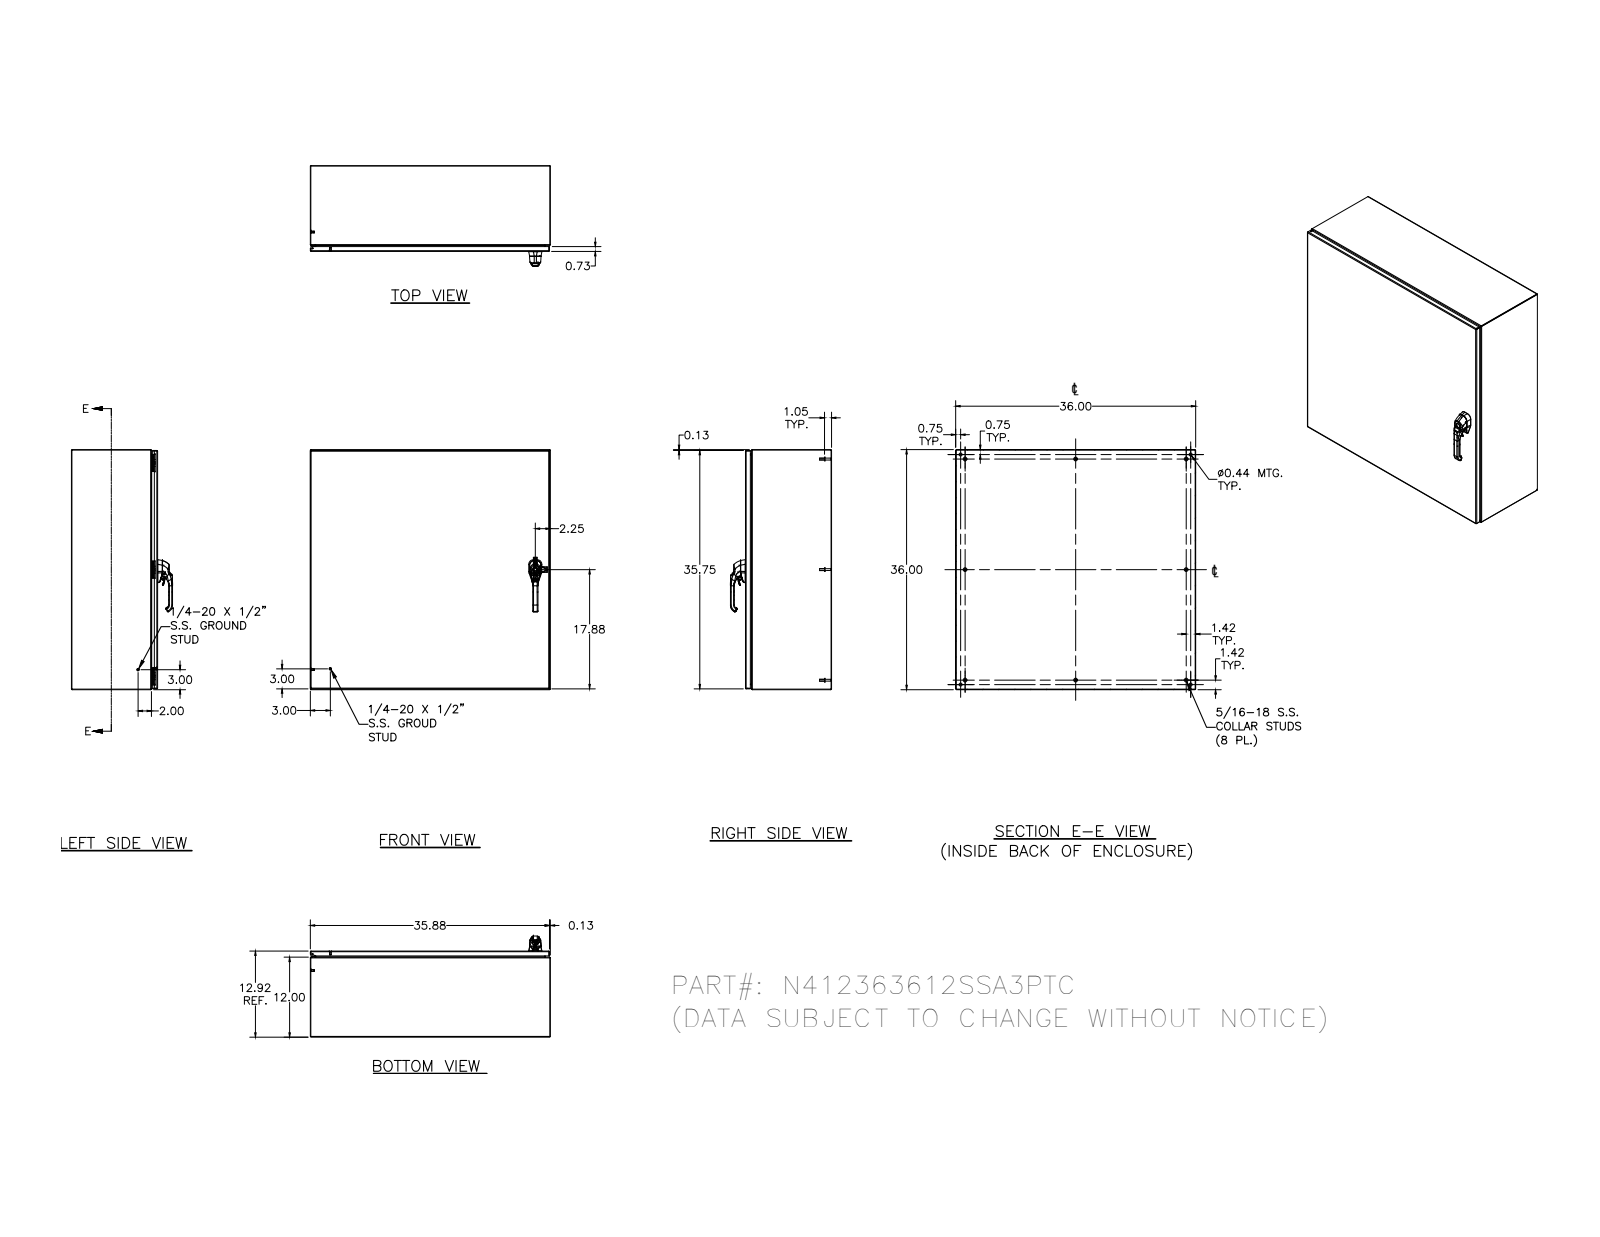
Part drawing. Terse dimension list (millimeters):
name: N412363612SSA3PTC; N412363612SSA3PTCBTB; N4123612SSA3PTCLS; N4123612SSA3PTCRS (+8 more)
written by: Autodesk Inventor 2011 (AUTOMOTIVE_DESIGN)
unit: mm
bodies: 72 solids, 3436 faces (1153 planar, 1265 cylindrical, 1018 other)
size: 914.4 × 914.4 × 385.2
volume: 5 752 000 mm³; area: 6 057 000 mm²
holes: 6× ⌀2.4, 6× ⌀3.9, 6× ⌀4.2, 6× ⌀4.4, 6× ⌀4.7, 5× ⌀4.2, 4× ⌀11.1, 3× ⌀4, 3× ⌀5.4, 2× ⌀2.7, 2× ⌀4.1, 2× ⌀4.3
bosses: 14× ⌀6.4, 8× ⌀14.3, 8× ⌀7.6, 8× ⌀7, 6× ⌀9.1, 6× ⌀8.1, 6× ⌀6.5, 6× ⌀4.2
rounds: 188× R0.5, 100× R0.3, 38× R1.3, 32× R0.8, 26× R0.4, 24× R3.2, 23× R0.5, 18× R2.7
face distances: 1.9, 326.2, 912.5, 328.1, 324.3, 910.6, 914.4, 302.9, 23.3, 893.7
hole spacings: 406.4, 812.8, 406.6, 876.3, 12.7, 16.7, 16.8, 33.2
